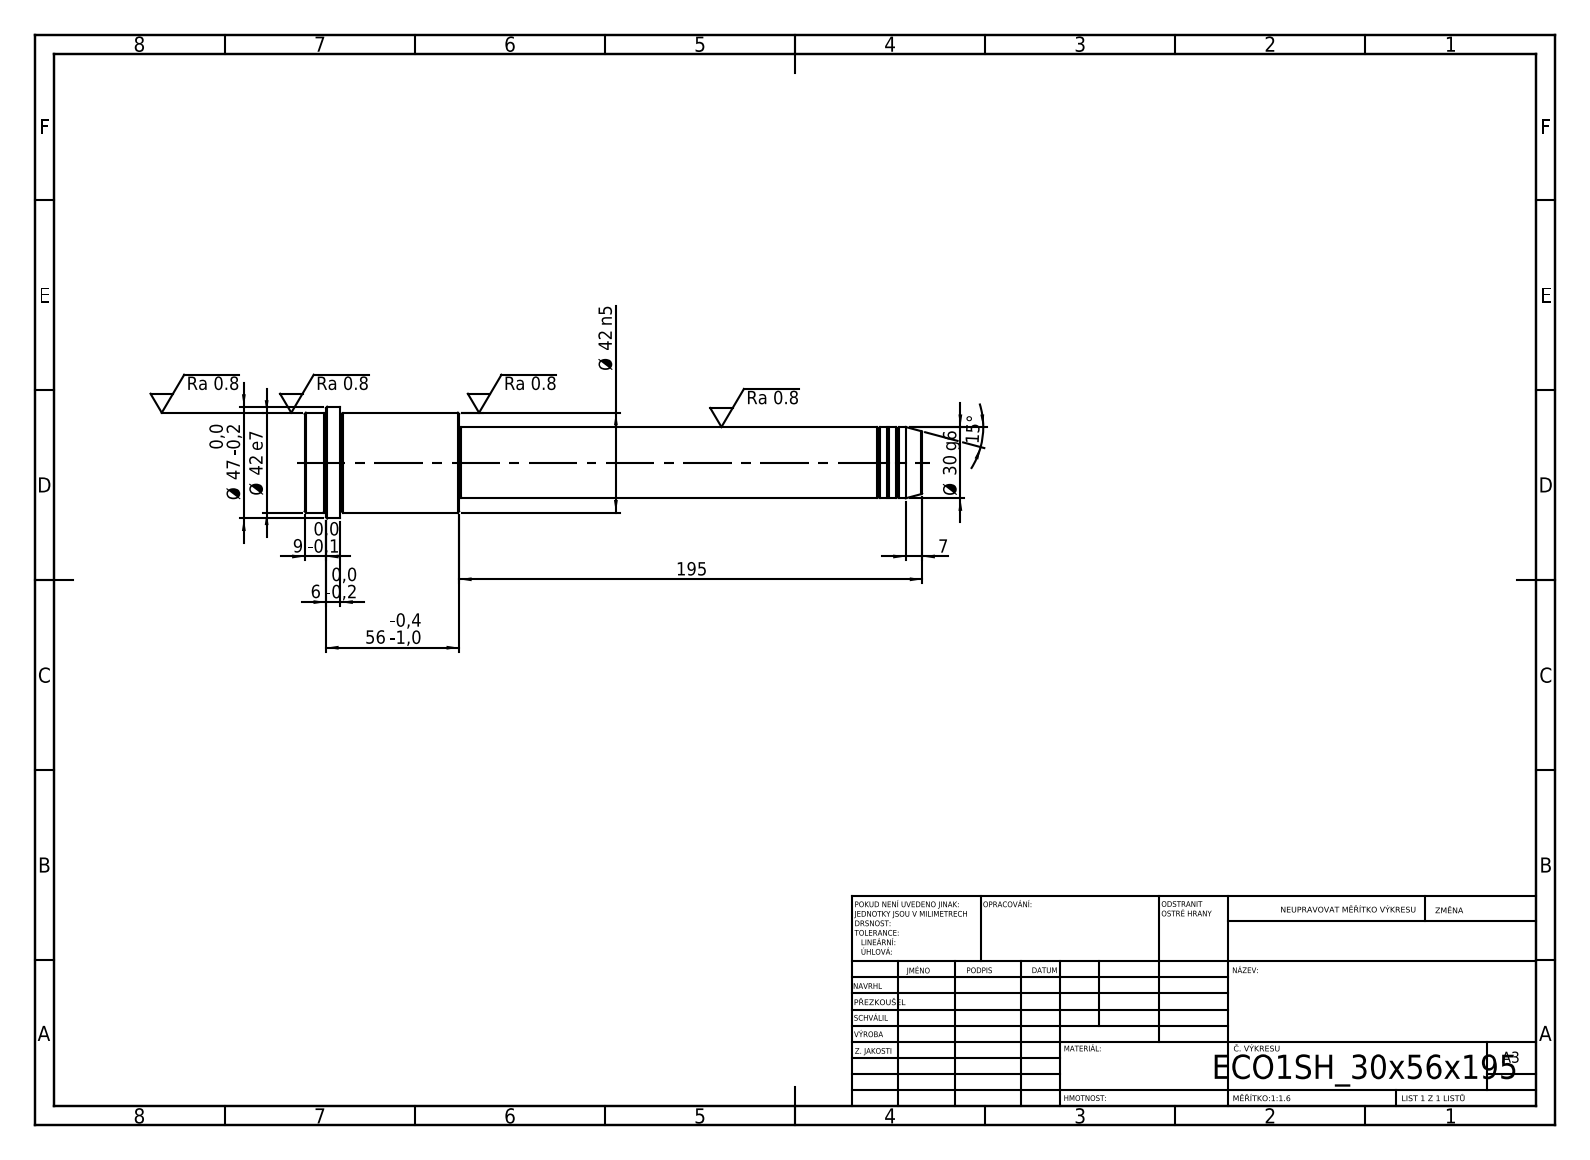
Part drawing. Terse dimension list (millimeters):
written by: SolidWorks 2019 (CONFIG_CONTROL_DESIGN)
unit: mm
bodies: 1 solid, 52 faces (6 planar, 16 cylindrical, 30 other)
size: 260 × 47 × 47
volume: 229 083 mm³; area: 30 589 mm²
bosses: 1× ⌀47, 1× ⌀42, 1× ⌀30, 1× ⌀29
face distances: 65, 195, 260, 245, 50, 15, 251, 56, 6, 9
